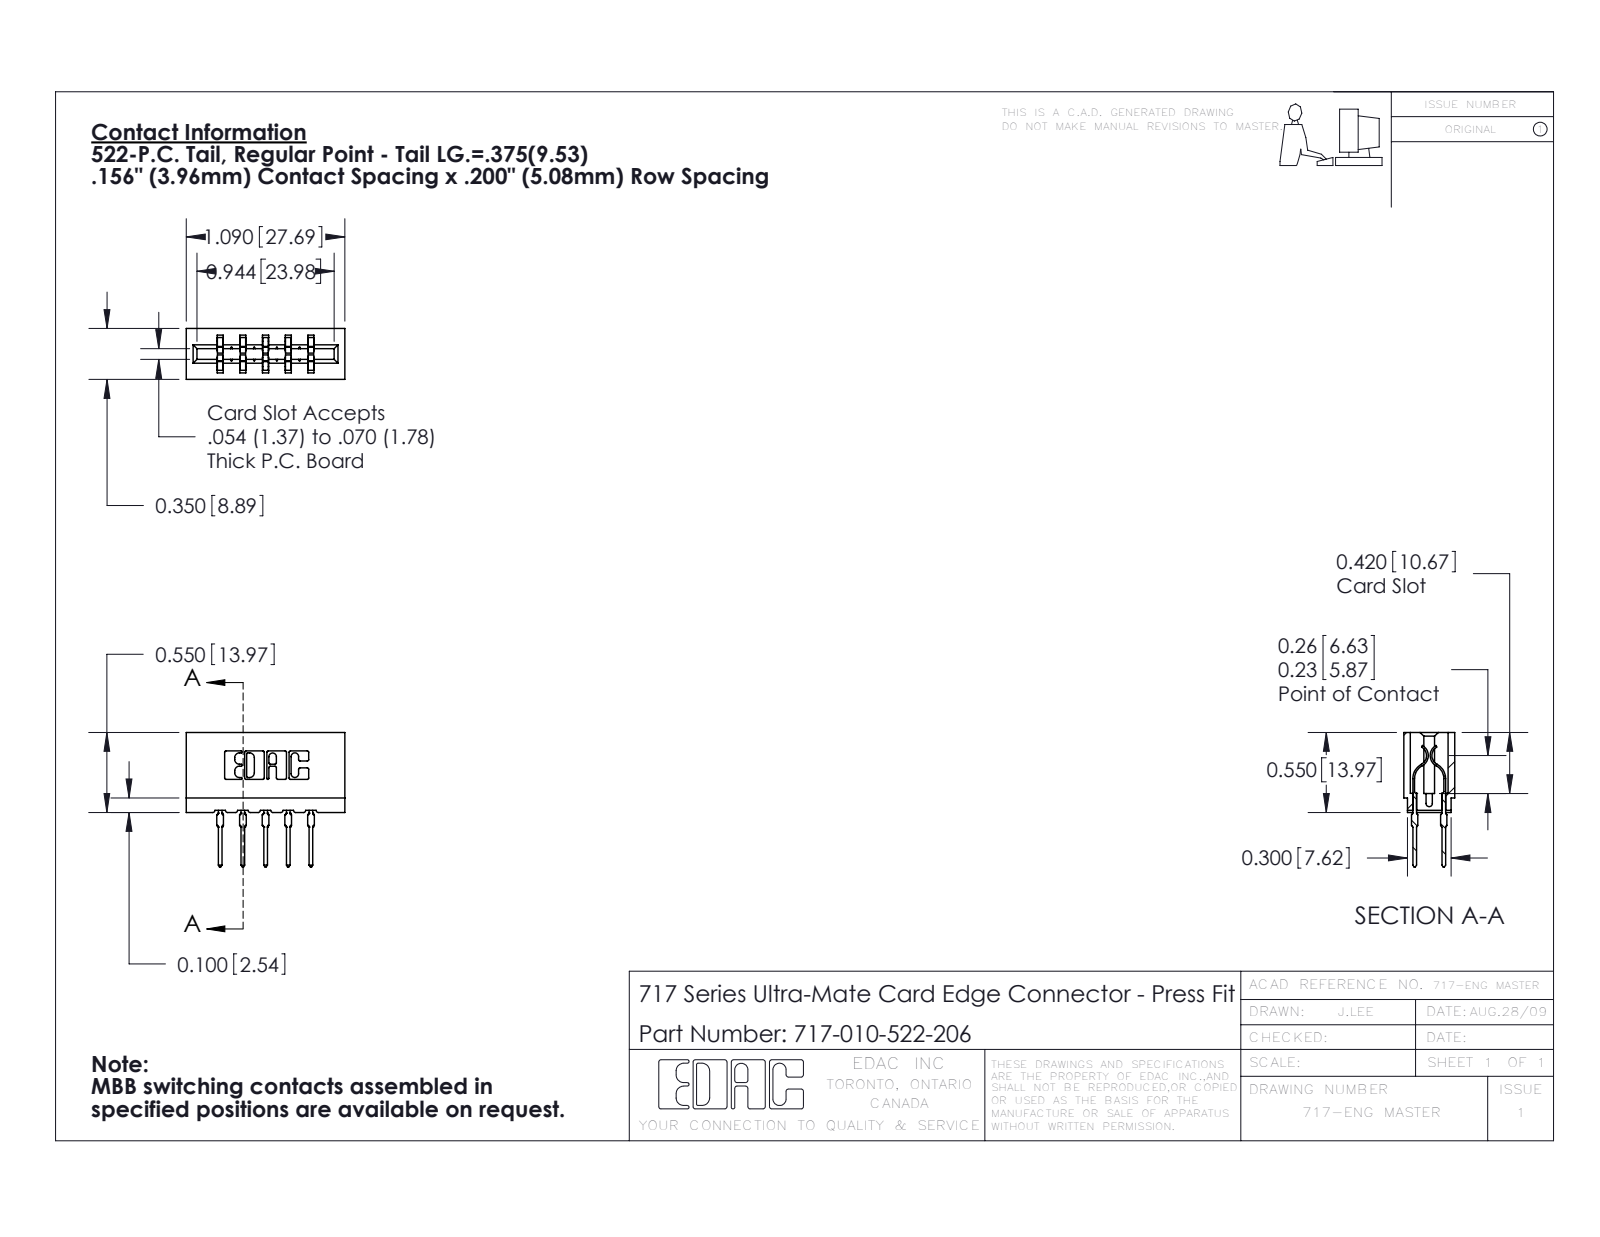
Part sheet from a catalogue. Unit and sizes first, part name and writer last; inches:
Units: inches
Overall size (bounding box): 1.09 × 0.924 × 0.35
Partial cylindrical surfaces — rounded edges, fillets, slot ends (radius × count): R0.01 ×22, R0.021 ×20, R0.015 ×10, R0.005 ×8, R0.011 ×8, R0.007 ×6, R0.031 ×6, R0.026 ×3
Main face-to-face distances: 0.212, 0.156, 0.138, 0.35, 0.198, 0.042, 0.312, 0.312, 0.468, 0.074
Volume: 0.156 in³ · Surface area: 5.367 in²
Bodies: 11 solids, 994 faces (519 planar, 215 cylindrical, 260 other)
Part name (STEP PRODUCT): 745-292-001_522; 717-010-522-206; 717 Part_Insulator Option - 06
STEP written by: SolidWorks 2016 (CONFIG_CONTROL_DESIGN)
